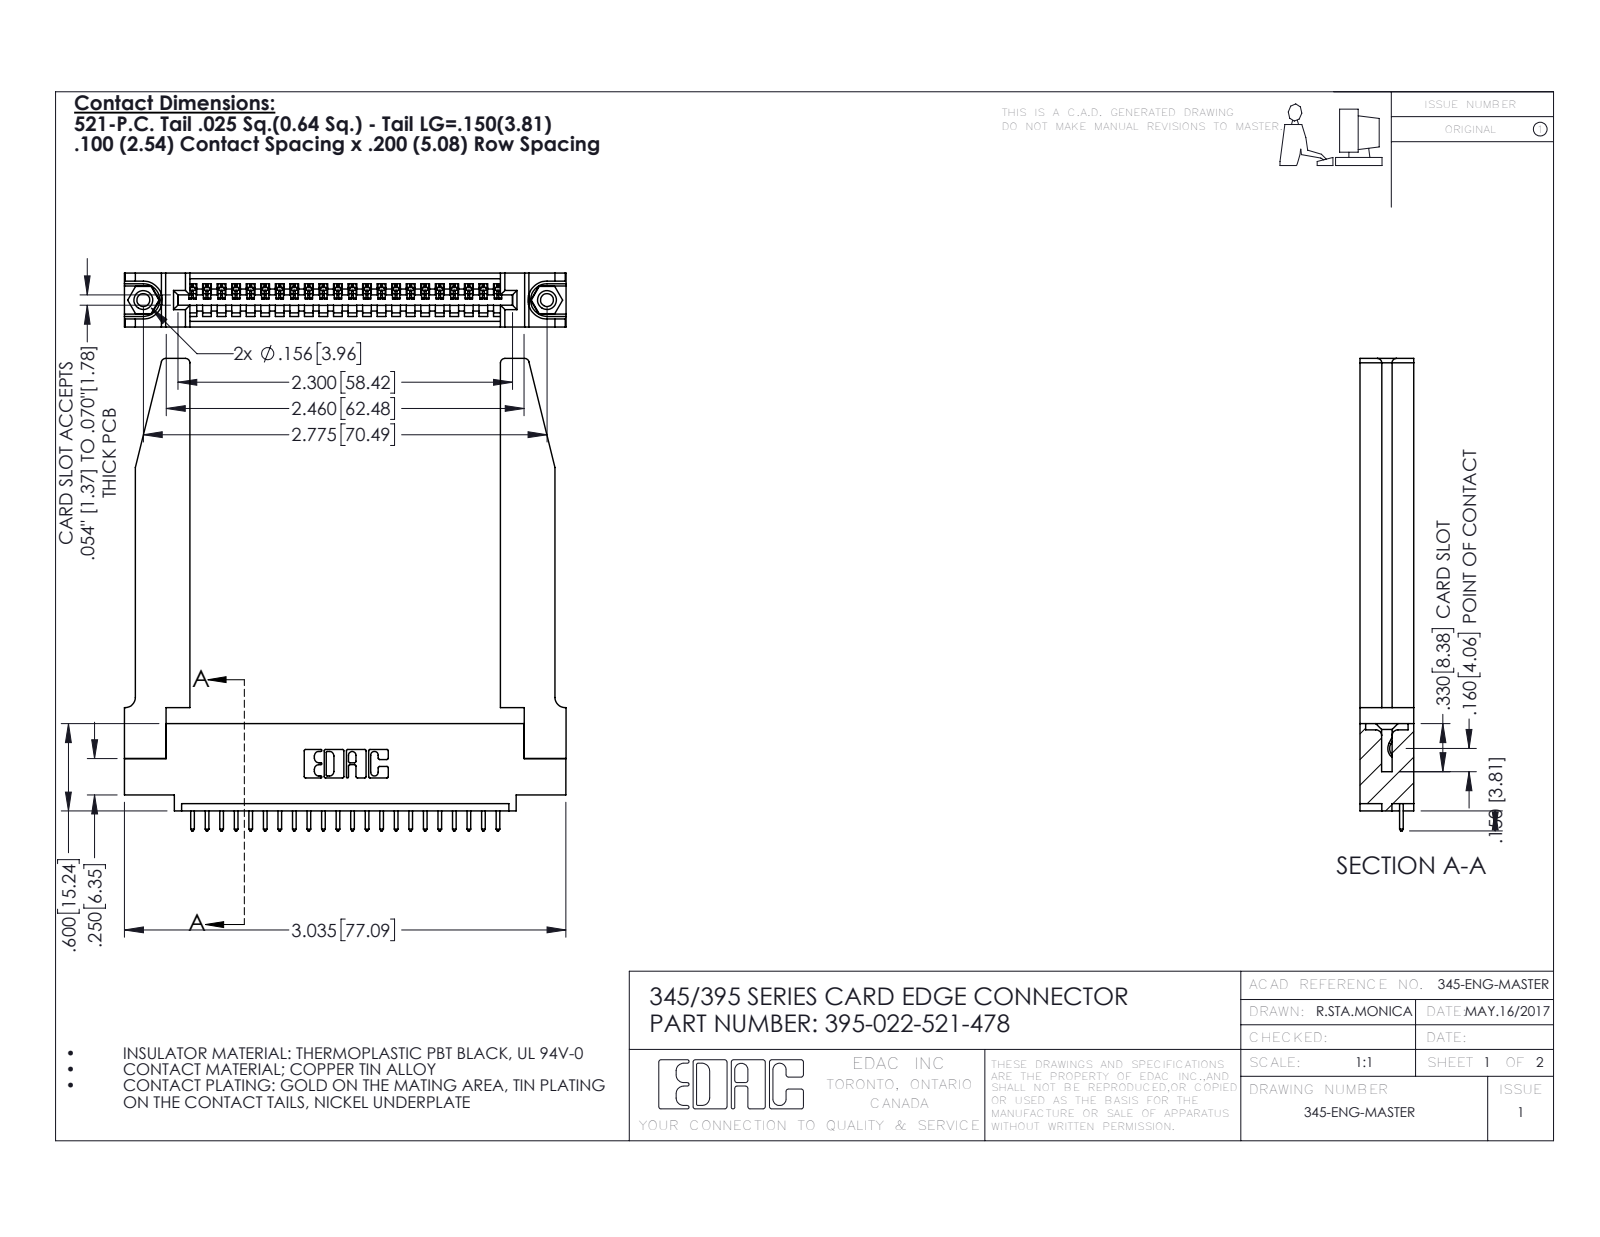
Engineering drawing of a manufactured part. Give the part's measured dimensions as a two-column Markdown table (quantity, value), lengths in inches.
| quantity | value |
| --- | --- |
| part name | 395-022-521-478; 345-220-078_345-220-078; 345 Part_0.110 Offset - 0.156 Dia-TH; 345-250-001_345-250-001-102 (+1 more) |
| STEP written by | SolidWorks 2016 (CONFIG_CONTROL_DESIGN) |
| units | inches |
| bodies | 27 solids, 1640 faces (1106 planar, 482 cylindrical, 52 other) |
| overall size | 3.247 × 3.036 × 0.37 |
| volume | 0.903 in³ |
| surface area | 24.41 in² |
| round holes (diameter × count) | 0.089 × 2, 0.125 × 2, 0.156 × 2, 0.064 × 1 |
| round bosses / shafts (diameter × count) | 0.155 × 2 |
| partial cylindrical surfaces (radius × count) | 0.006 × 44, 0.01 × 44, 0.01 × 22, 0.03 × 8, 0.007 × 6, 0.031 × 6, 0.026 × 3, 0.031 × 2 |
| main face-to-face distances | 0.37, 0.072, 0.298, 0.2, 0.098, 0.272, 0.025, 0.148, 0.15, 0.22 |
| hole center spacings | 0.27, 2.541, 2.775 |
